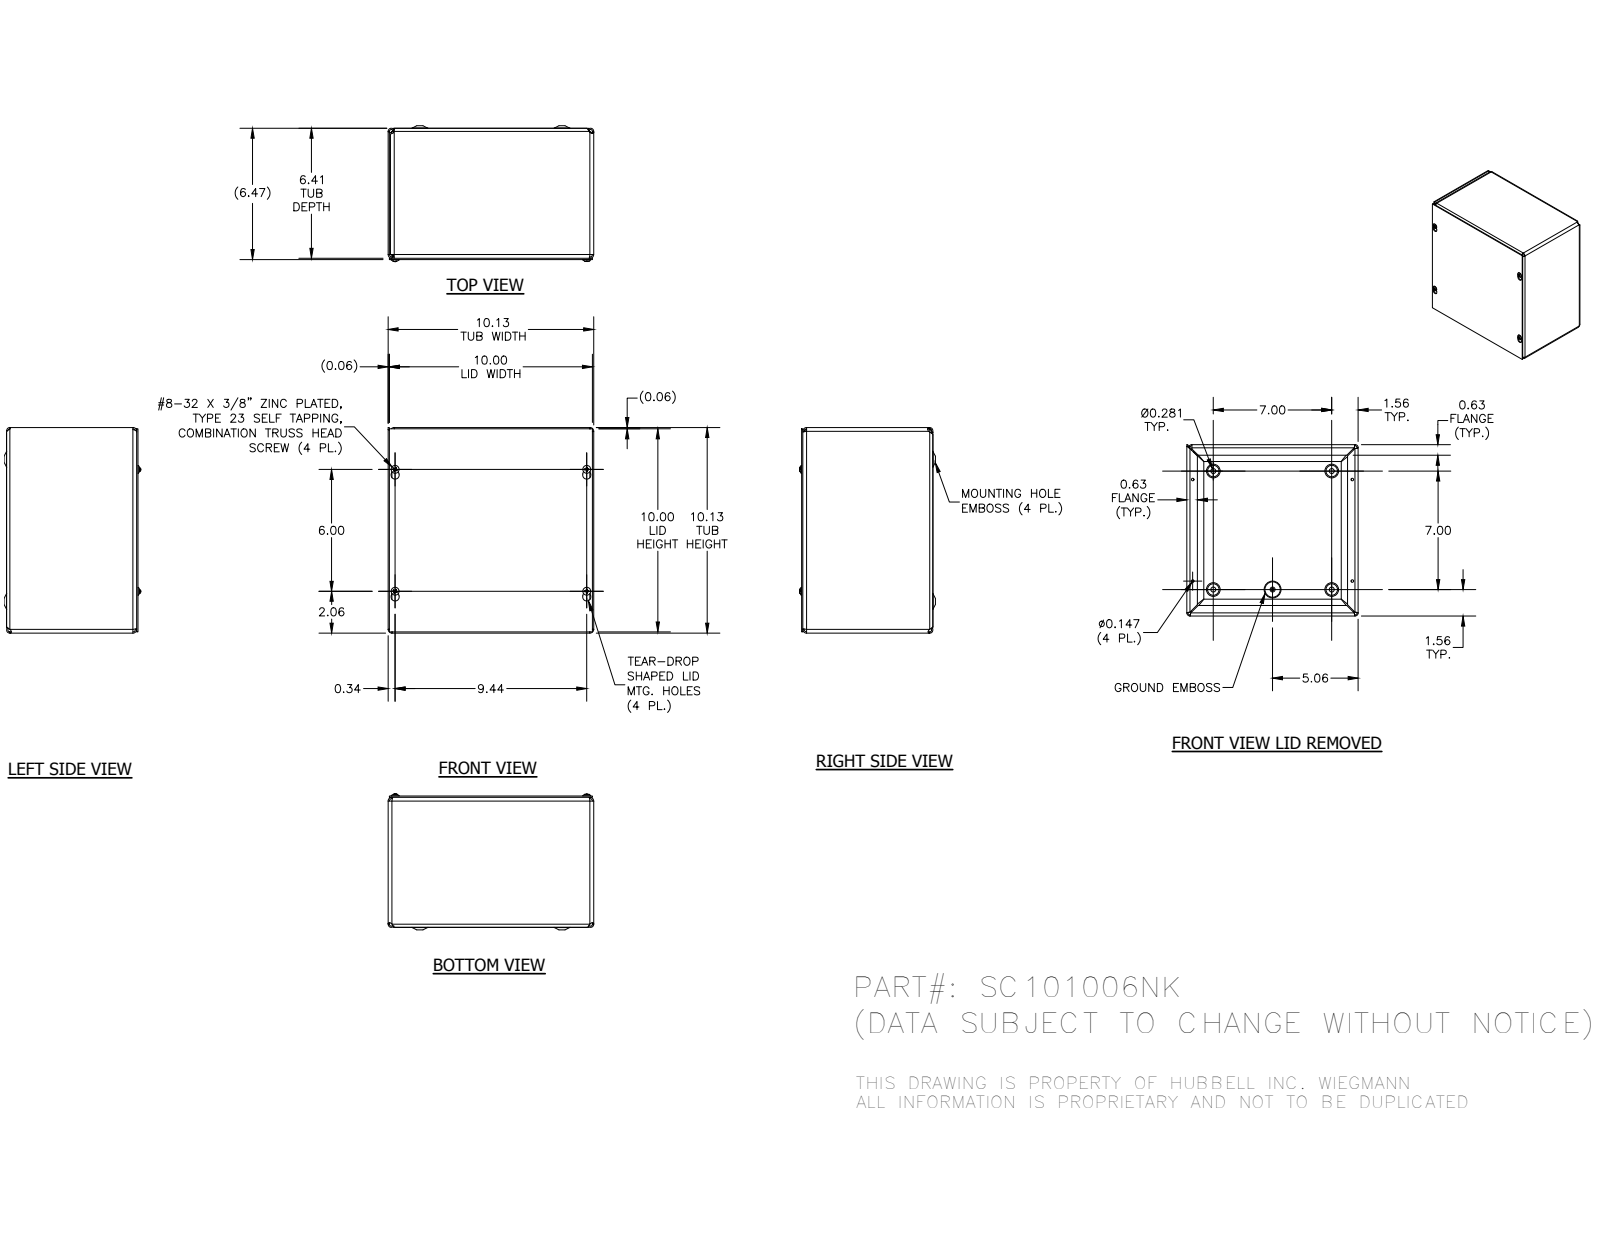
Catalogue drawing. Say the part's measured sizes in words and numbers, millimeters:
The part is named "SC1010BKP; SC101006NKWRA; SC1010LID; 34056 (+1 more)". Its 3-D file was written by "Autodesk Inventor 2014 (AUTOMOTIVE_DESIGN)". It is 7 solids with 357 faces: 132 planar, 67 cylindrical and 158 other. Overall it measures 257.18 by 257.18 by 170 millimeters. Its volume is 511 082 cubic millimeters and its surface area 656 301 square millimeters. Round holes: 4 of diameter 3.73, 4 of diameter 7.62, 1 of diameter 4.19. Round bosses or shafts: 4 of diameter 9.75, 4 of diameter 4.17, 1 of diameter 5.8. Partial cylindrical surfaces (rounded edges, fillets, slot ends): 12 of radius 3.17, 8 of radius 4.75, 4 of radius 1.4, 4 of radius 1.57, 4 of radius 2.38, 4 of radius 2.97, 4 of radius 3.15, 4 of radius 3.96. The main face-to-face distances are 1.57, 1.58, 161.12, 255.6, 257.18, 254.03, 255.61, 162.69, 1.59, 162.71. The hole center spacings are 167.98, 177.8, 33.45, 33.46, 88.9, 152.4, 198.79, 209.14.
